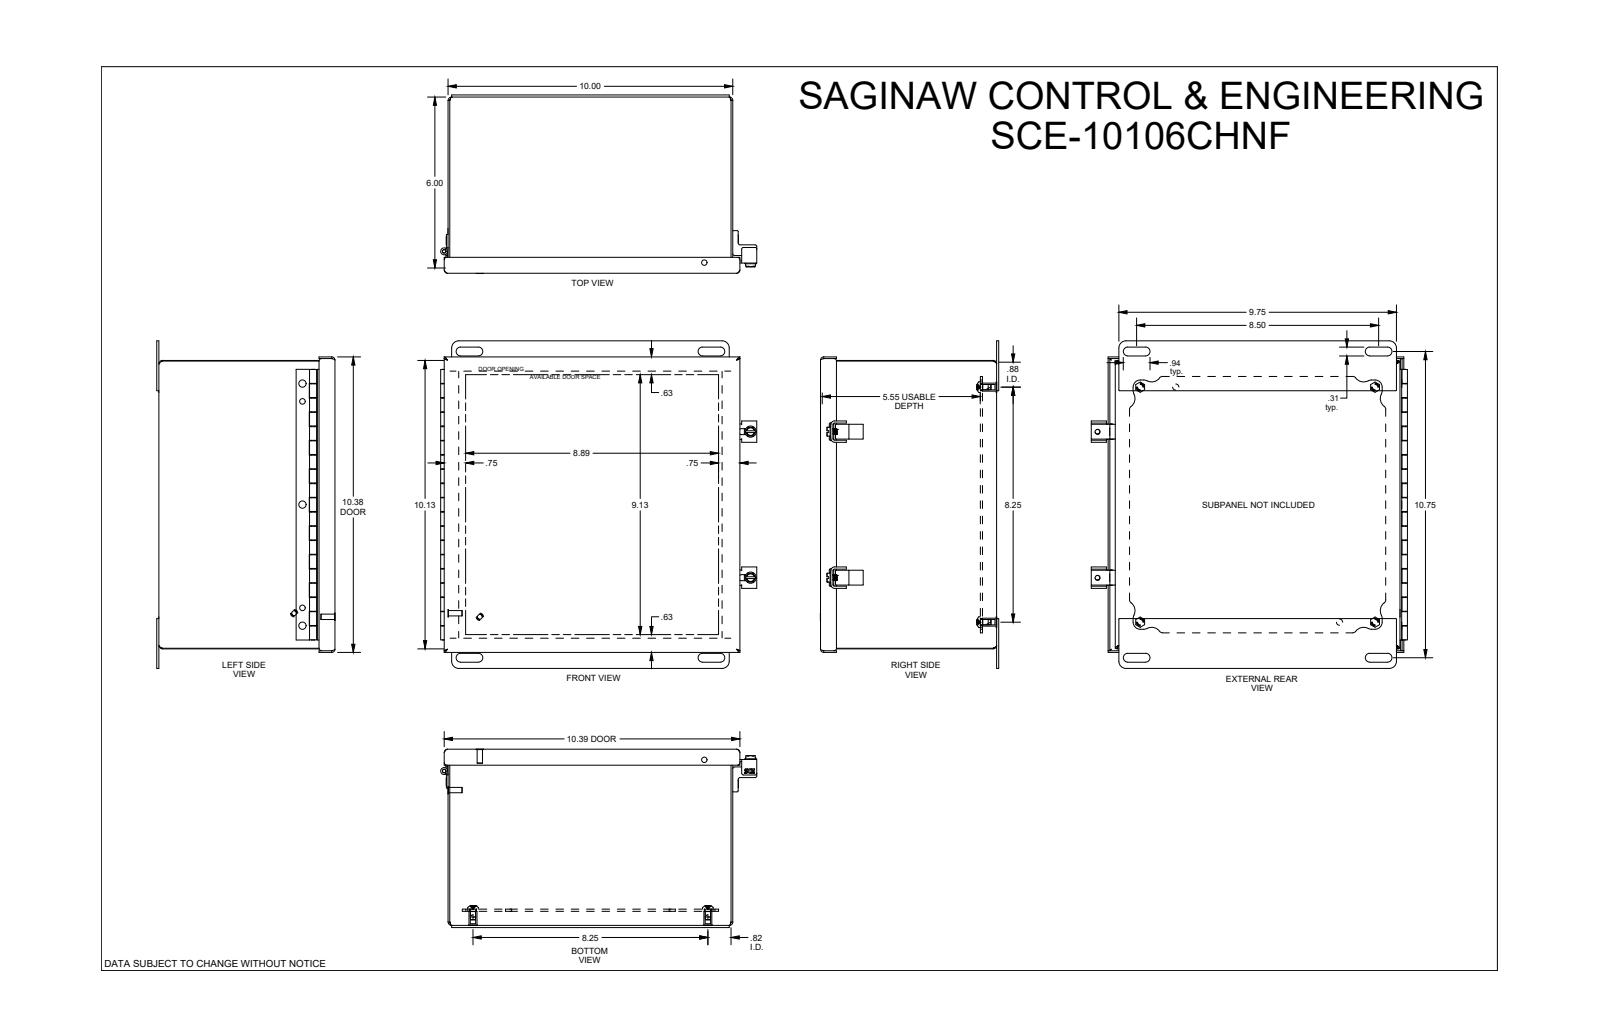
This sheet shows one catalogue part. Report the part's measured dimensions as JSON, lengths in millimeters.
{"part_name": "SCE-10106CHNF", "step_written_by": "SolidWorks 2019 (AUTOMOTIVE_DESIGN)", "units": "millimeters", "bodies": {"solids": 37, "faces": 1225, "planar": 537, "cylindrical": 341, "other": 347}, "overall_size": [292.1, 282, 159.1], "volume_mm3": 678800, "surface_area_mm2": 834800, "round_holes": [[4.8, 9], [4.9, 7], [6.4, 4], [7.1, 4], [4, 2], [5.5, 2], [6.8, 2], [3.2, 1], [4.7, 1]], "round_bosses_or_shafts": [[4.8, 11], [6.5, 7], [9.5, 4], [7.1, 4], [10.1, 2], [4.8, 2], [6.2, 1], [3.1, 1]], "partial_cylinders_radius": [[0.3, 76], [1.5, 33], [6.4, 16], [1.3, 8], [3.2, 8], [4, 8], [8.7, 8], [0.7, 6]], "face_to_face_distances": [1.5, 155.6, 252.5, 157.1, 154.1, 1.9, 1.5, 13, 11, 14.5], "hole_center_spacings": [296.3, 209.6, 209.5, 209.6, 296.3, 300.3, 211.9, 274.8]}
